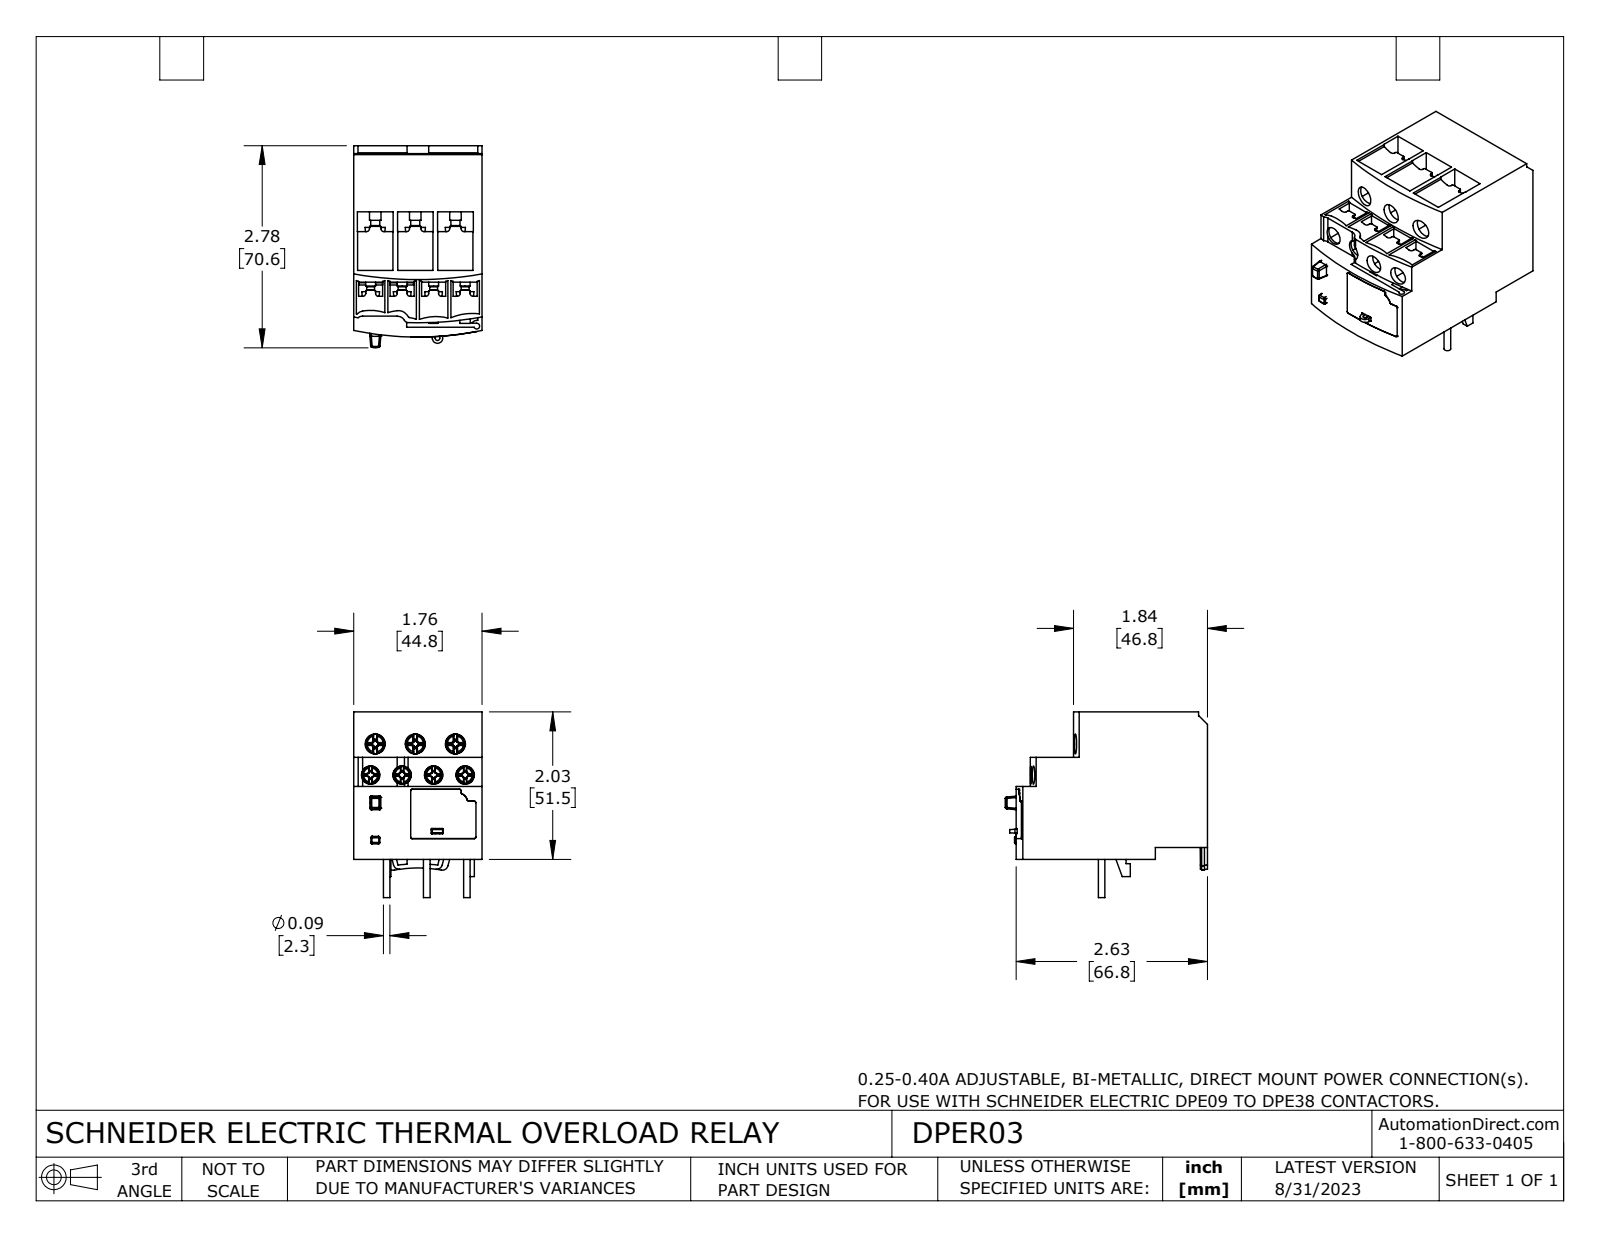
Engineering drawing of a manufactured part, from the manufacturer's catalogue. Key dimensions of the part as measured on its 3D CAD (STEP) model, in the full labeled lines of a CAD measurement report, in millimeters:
Part name (STEP PRODUCT): DPER03
STEP written by: SolidWorks 2021 (CONFIG_CONTROL_DESIGN)
Units: millimetres
Bodies: 16 solids, 1212 faces (676 planar, 269 cylindrical, 267 other)
Overall size (bounding box): 70.6 × 64.8 × 44.8
Volume: 113 900 mm³ · Surface area: 30 420 mm²
Round holes (diameter × count): ⌀6.4 ×4, ⌀7 ×3, ⌀2 ×2, ⌀3 ×2, ⌀1.5 ×1, ⌀6.2 ×1
Round bosses / shafts (diameter × count): ⌀2.3 ×12, ⌀3.5 ×4, ⌀2.7 ×4, ⌀4 ×3, ⌀3.9 ×3, ⌀3.1 ×3, ⌀3 ×1, ⌀2.7 ×1
Partial cylindrical surfaces — rounded edges, fillets, slot ends (radius × count): R0.5 ×52, R1 ×22, R0.1 ×19, R0.3 ×8, R0.2 ×6, R16 ×6, R2 ×4, R0.6 ×2
Main face-to-face distances: 44.8, 4.2, 51.5, 47.3, 23.1, 14, 15.7, 35.8, 31.6, 63.4
Hole centre spacings: 11, 14, 22, 8.5, 9.7, 10.3, 10.7, 11.4
